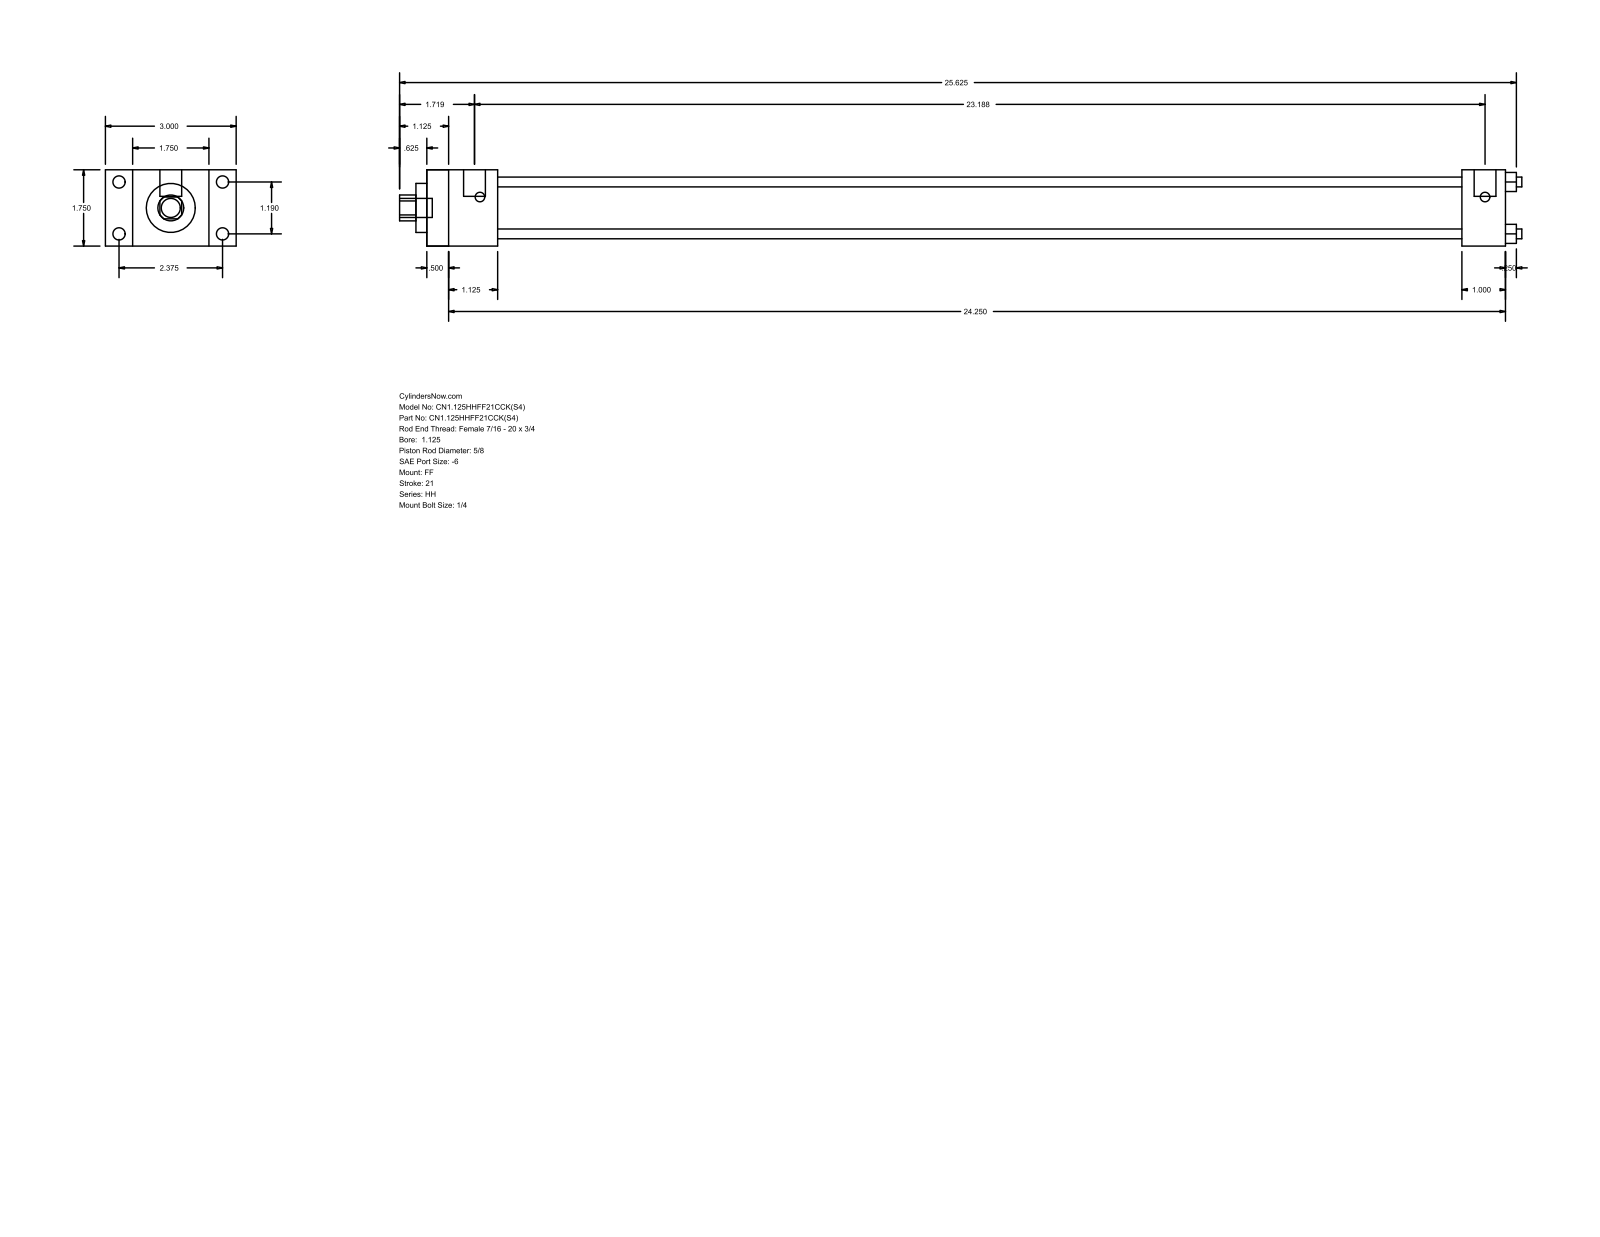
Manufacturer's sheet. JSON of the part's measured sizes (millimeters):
{"part_name": "HH_FF__0112_0.625", "step_written_by": "GSSL Pune (CONFIG_CONTROL_DESIGN)", "units": "millimeters", "bodies": {"solids": 0, "faces": 92, "planar": 64, "cylindrical": 28, "other": 0}, "overall_size": [654.05, 76.2, 44.45], "round_holes": [[5.71, 4], [15.88, 1], [28.57, 1], [34.92, 1]], "round_bosses_or_shafts": [[7.14, 4], [5.56, 4], [12.7, 2], [11.11, 1]], "partial_cylinders_radius": [[7.54, 1]], "face_to_face_distances": [44.46, 628.64, 12.69, 615.95, 15.87, 60.33, 28.58, 41.27, 603.24, 590.55], "hole_center_spacings": [21.37, 30.22, 42.74]}
